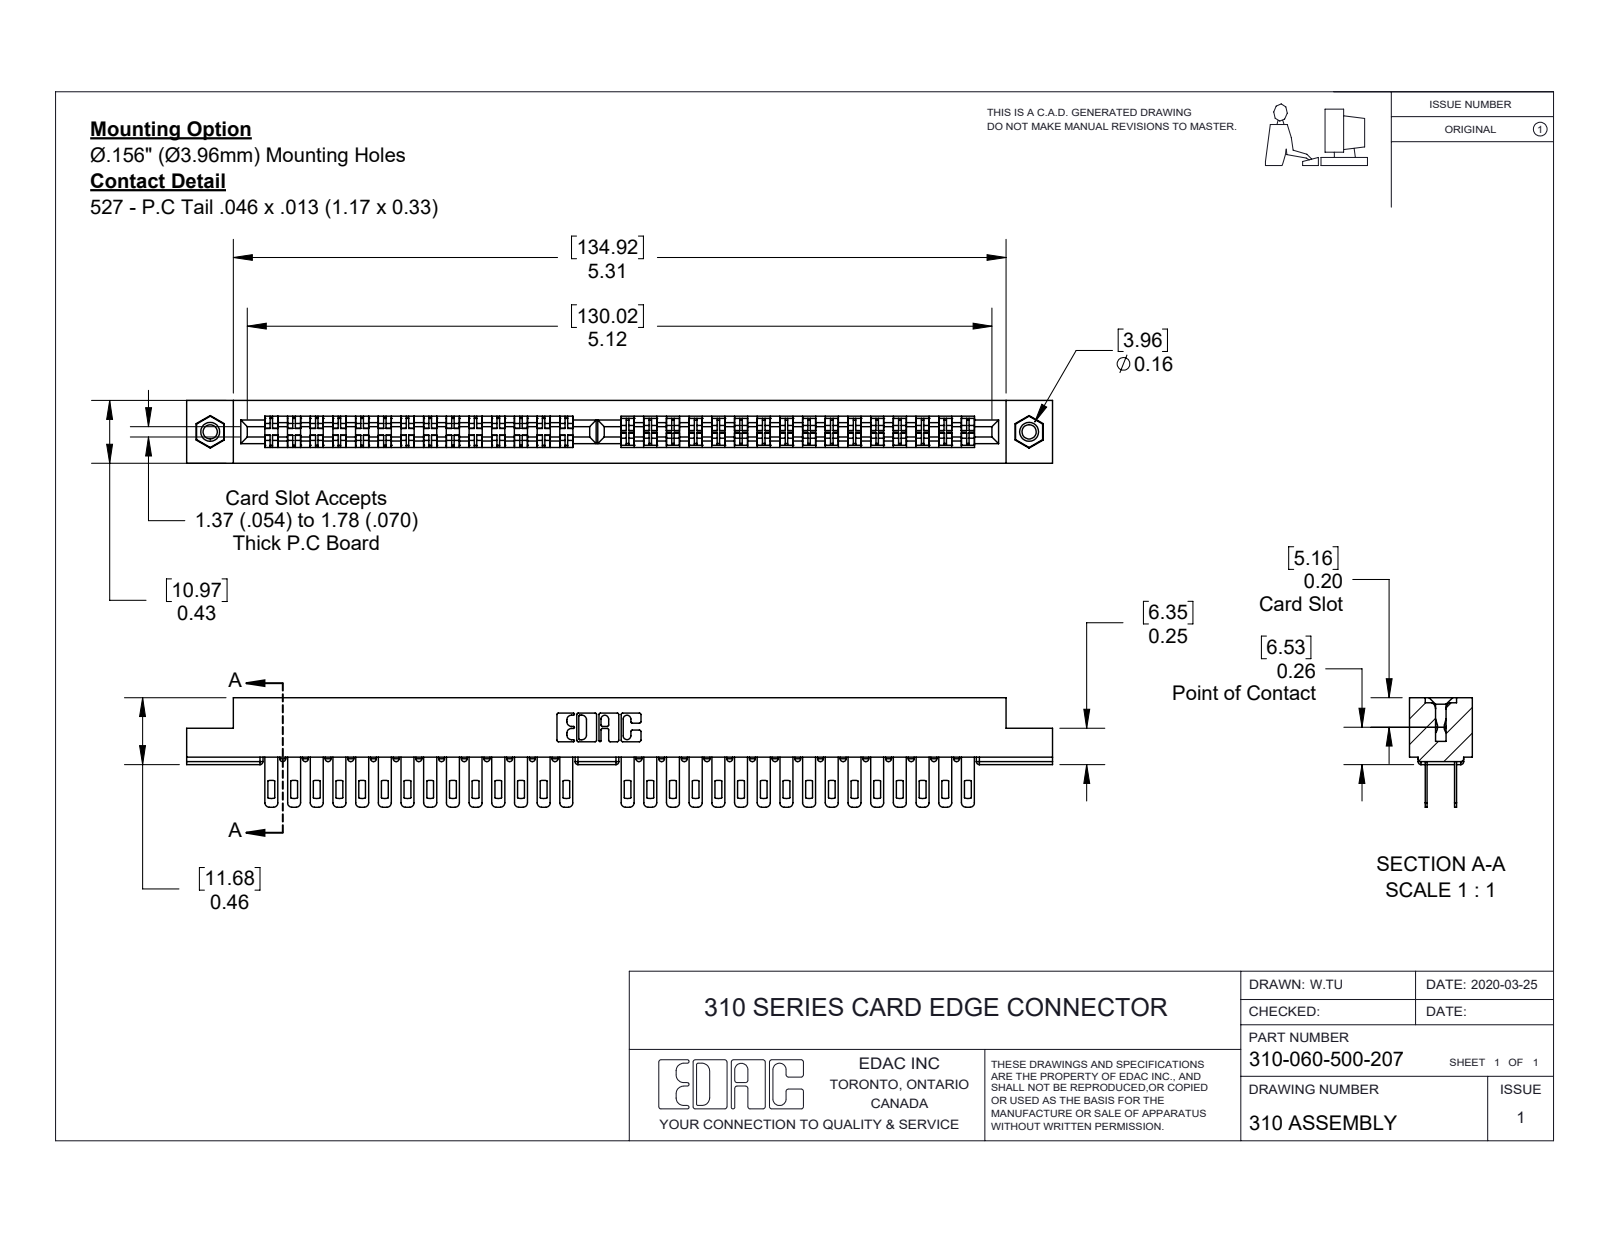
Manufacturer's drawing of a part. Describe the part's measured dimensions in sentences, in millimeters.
The part is named "345-250-001_345-250-005-103; 307-290-001_500; 310-060-500-207; 310 Part_.116 Hex". Its 3-D file was written by "SolidWorks 2016 (CONFIG_CONTROL_DESIGN)". It is 63 solids with 2986 faces: 1916 planar, 990 cylindrical and 80 other. Overall it measures 151.21 by 19.13 by 10.97 millimeters. Its volume is 13 169 cubic millimeters and its surface area 18 961 square millimeters. Round holes: 2 of diameter 2.5, 2 of diameter 3.17, 2 of diameter 3.96. Round bosses or shafts: 2 of diameter 3.94. Partial cylindrical surfaces (rounded edges, fillets, slot ends): 98 of radius 0.51, 60 of radius 0.76, 30 of radius 1.59, 22 of radius 0.25, 6 of radius 0.17, 6 of radius 0.8, 4 of radius 0.3, 4 of radius 0.64. The main face-to-face distances are 2.76, 8.22, 0.33, 0.38, 4.75, 10.98, 5.08, 3.14, 7.84, 5.46. The hole center spacings are 143.
